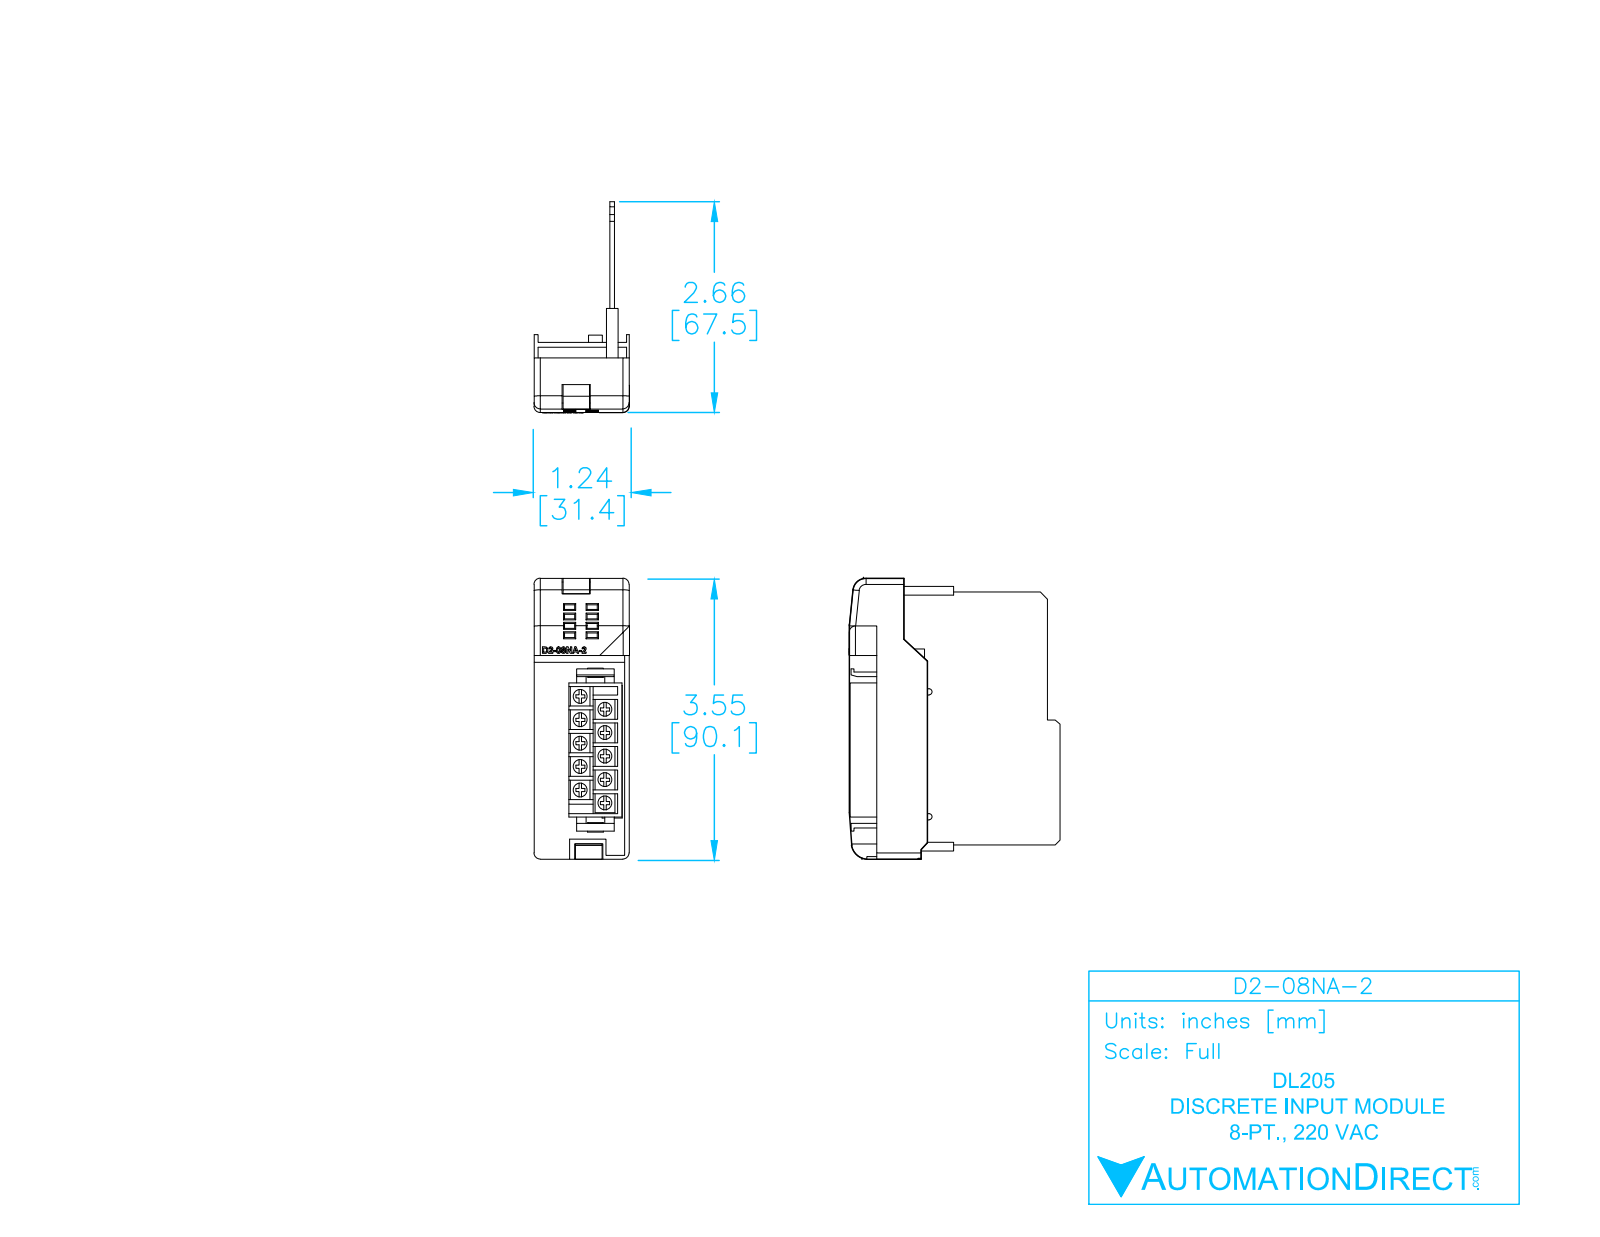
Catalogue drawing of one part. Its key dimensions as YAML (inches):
part_name: "D2-08NA-2_ModuleCase_light_NEW"
step_written_by: "SolidWorks 2009 (AUTOMOTIVE_DESIGN)"
units: inches
bodies: {solids: 6, faces: 586, planar: 411, cylindrical: 75, other: 100}
overall_size: [3.543, 2.66, 1.203]
volume: 1.548
surface_area: 44.22
round_bosses_or_shafts:
  - {diameter: 0.177, count: 10}
partial_cylinders:
  - {radius: 0.014, count: 16}
  - {radius: 0.079, count: 9}
  - {radius: 0.01, count: 2}
  - {radius: 0.039, count: 2}
  - {radius: 0.049, count: 2}
  - {radius: 0.162, count: 1}
  - {radius: 0.212, count: 1}
face_to_face_distances: [0.059, 0.186, 0.245, 0.143, 0.083, 0.102, 0.127, 0.043, 0.32, 0.956]
